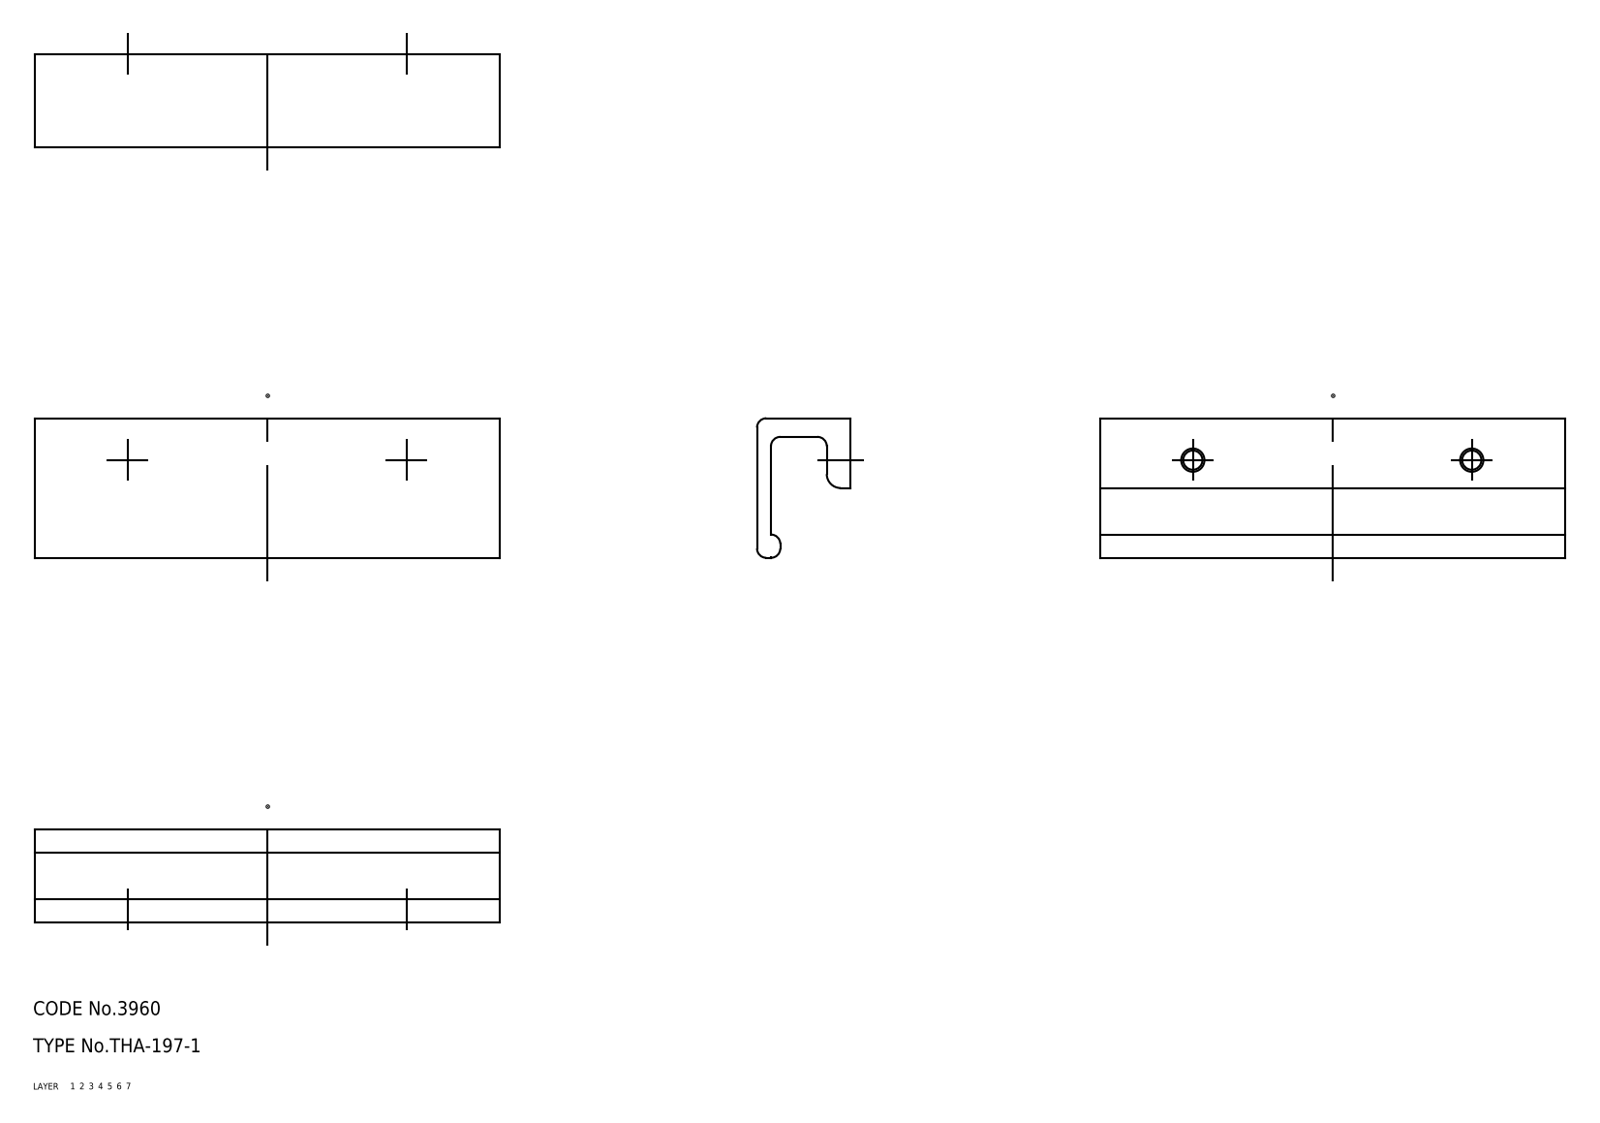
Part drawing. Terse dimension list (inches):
name: pull
written by: CADfix (AUTOMOTIVE_DESIGN)
unit: in
bodies: 1 solid, 22 faces (0 planar, 0 cylindrical, 22 other)
size: 3.937 × 1.181 × 0.787
volume: 1.327 in³; area: 19.33 in²
